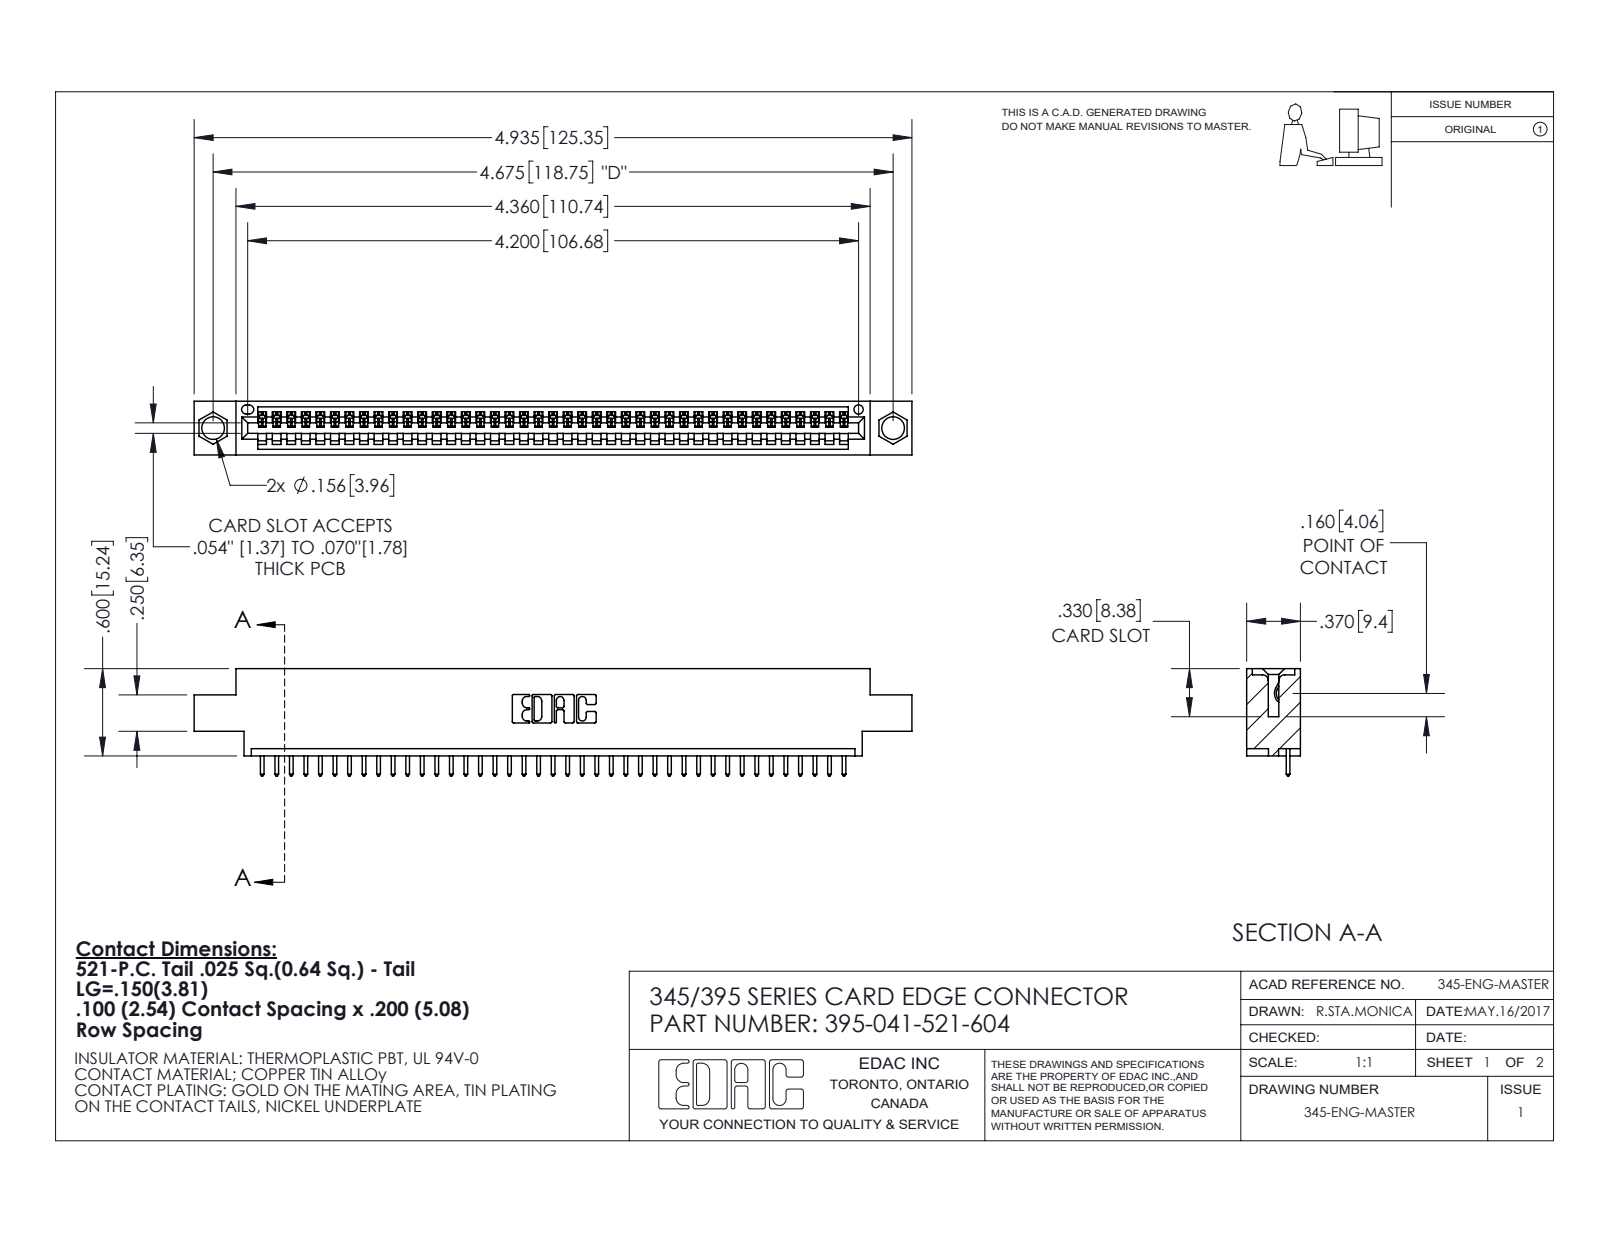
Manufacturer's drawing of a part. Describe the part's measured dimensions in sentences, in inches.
The part is named "395-041-521-604; 345 Part_0.170 Offset - 0.156 Dia-TI; 345-292-001_345-293-121". Its 3-D file was written by "SolidWorks 2020 (CONFIG_CONTROL_DESIGN)". It is 42 solids with 2522 faces: 1738 planar, 784 cylindrical and 0 other. Overall it measures 4.935 by 0.737 by 0.37 inches. Its volume is 0.706 cubic inches and its surface area 23.04 square inches. Round holes: 2 of diameter 0.156, 1 of diameter 0.064. Partial cylindrical surfaces (rounded edges, fillets, slot ends): 82 of radius 0.006, 82 of radius 0.01, 22 of radius 0.01, 6 of radius 0.007, 6 of radius 0.031, 3 of radius 0.026, 2 of radius 0.031, 2 of radius 0.04. The main face-to-face distances are 0.072, 0.298, 0.37, 0.2, 0.098, 0.272, 0.025, 0.225, 0.175, 0.149. The hole center spacings are 0.27, 4.439, 4.675.
